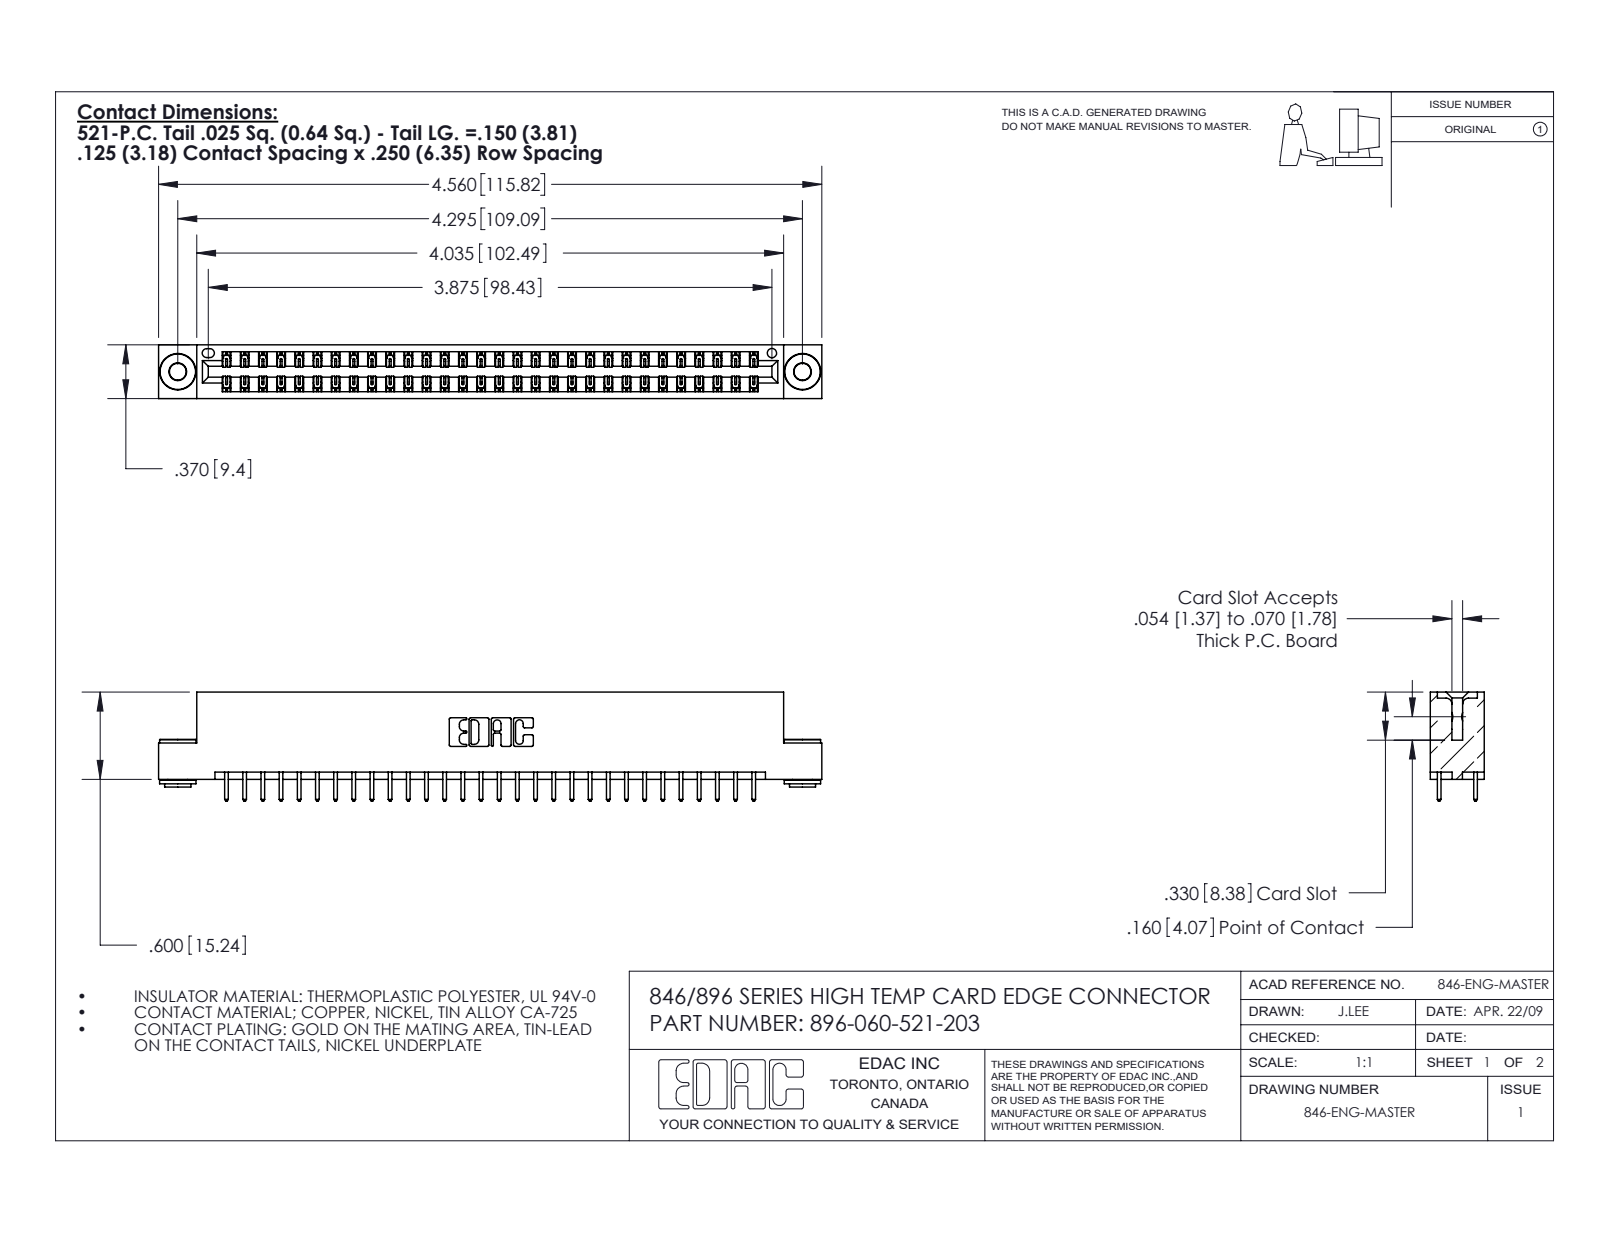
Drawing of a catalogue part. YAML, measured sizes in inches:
part_name: "345-292-001_345-293-121; 345-250-002_345-250-002-102; 396-060-521-203; 346 Part_Flush Mounting Lugs - 0.156 Dia-TH"
step_written_by: "SolidWorks 2016 (CONFIG_CONTROL_DESIGN)"
units: inches
bodies: {solids: 63, faces: 3280, planar: 2186, cylindrical: 1086, other: 8}
overall_size: [4.56, 0.75, 0.37]
volume: 0.683
surface_area: 23.64
round_holes:
  - {diameter: 0.116, count: 2}
  - {diameter: 0.156, count: 2}
  - {diameter: 0.064, count: 1}
round_bosses_or_shafts:
  - {diameter: 0.25, count: 2}
  - {diameter: 0.18, count: 2}
  - {diameter: 0.136, count: 2}
partial_cylinders:
  - {radius: 0.006, count: 90}
  - {radius: 0.01, count: 60}
  - {radius: 0.01, count: 22}
  - {radius: 0.007, count: 6}
  - {radius: 0.031, count: 6}
  - {radius: 0.026, count: 3}
  - {radius: 0.014, count: 2}
  - {radius: 0.022, count: 2}
face_to_face_distances: [0.048, 0.322, 0.25, 0.37, 0.025, 0.072, 0.298, 0.275, 0.148, 0.222]
hole_center_spacings: [0.246, 4.087, 4.295]
